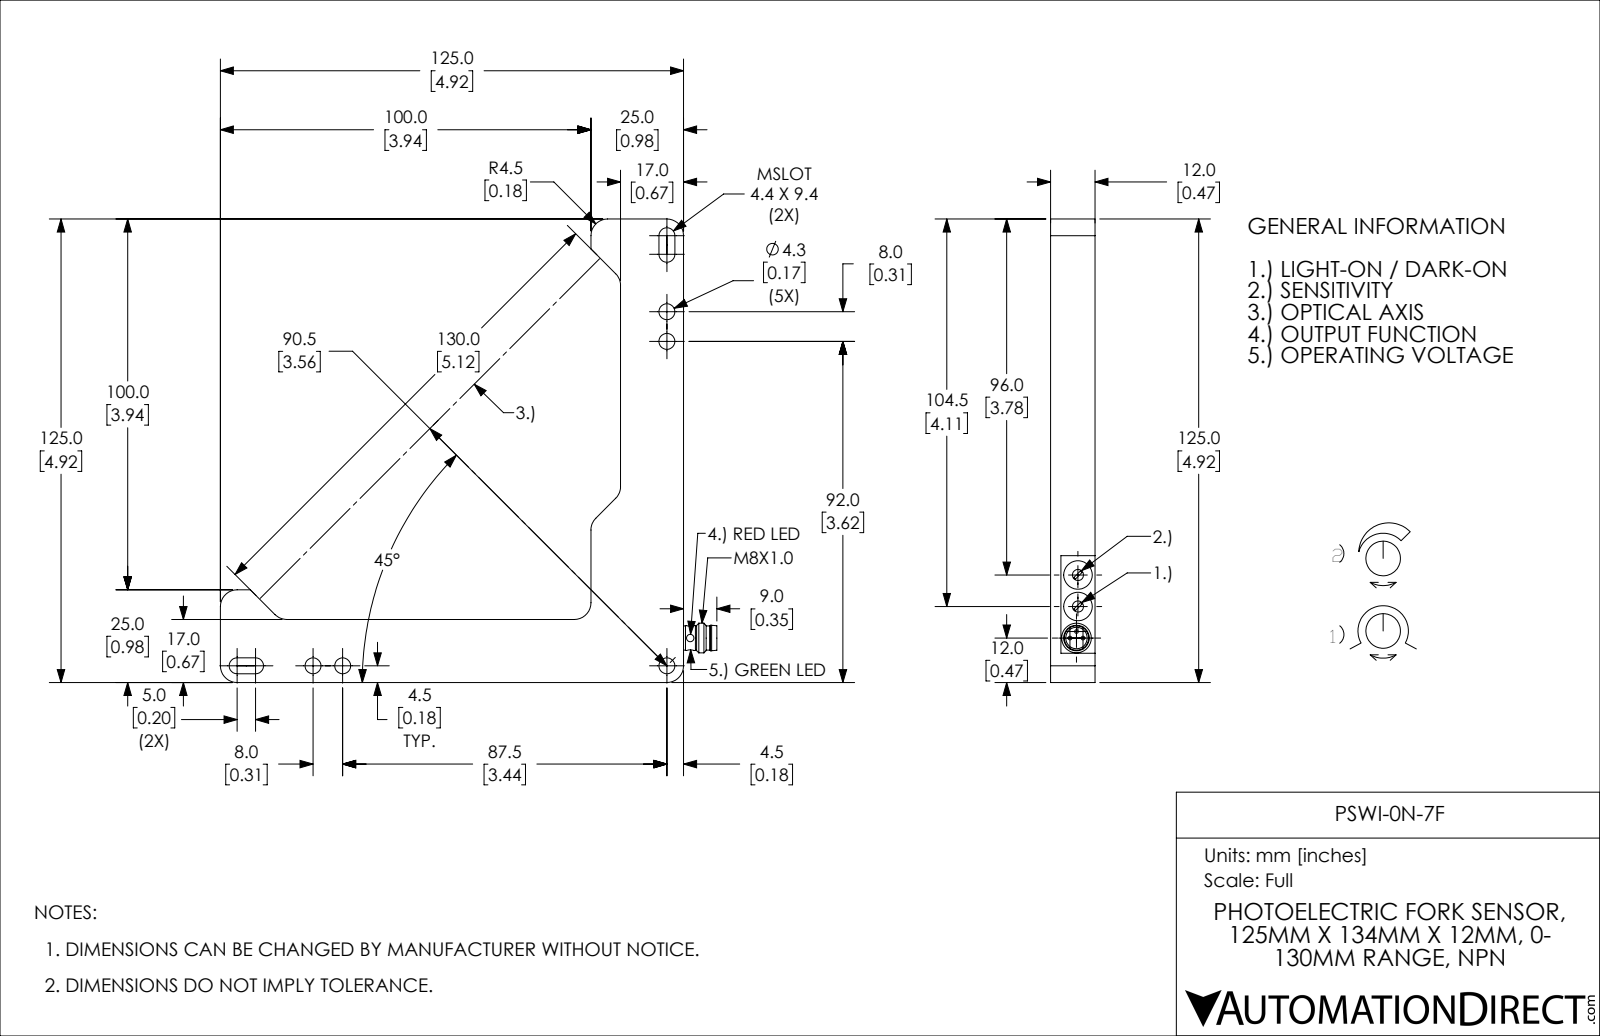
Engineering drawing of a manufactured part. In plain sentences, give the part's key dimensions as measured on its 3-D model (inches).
The part is named "PSWI-0N-7F". Its 3-D file was written by "SolidWorks 2017 (AUTOMOTIVE_DESIGN)". It is 1 solid with 91 faces: 43 planar, 41 cylindrical and 7 other. Overall it measures 5.276 by 4.921 by 0.472 inches. Its volume is 3.111 cubic inches and its surface area 25.24 square inches. Round holes: 5 of diameter 0.169, 2 of diameter 0.079, 2 of diameter 0.118, 2 of diameter 0.303, 1 of diameter 0.228. Round bosses or shafts: 3 of diameter 0.039, 1 of diameter 0.315, 1 of diameter 0.272, 1 of diameter 0.264, 1 of diameter 0.257. Partial cylindrical surfaces (rounded edges, fillets, slot ends): 10 of radius 0.177, 4 of radius 0.085, 2 of radius 0.049. The main face-to-face distances are 0.472, 0.669, 4.921, 4.252, 0.984, 0.315, 3.937, 0.262, 0.407, 4.659. The hole center spacings are 0.315, 3.445, 3.76, 5.099, 0.335, 0.335, 0.385, 0.669.
